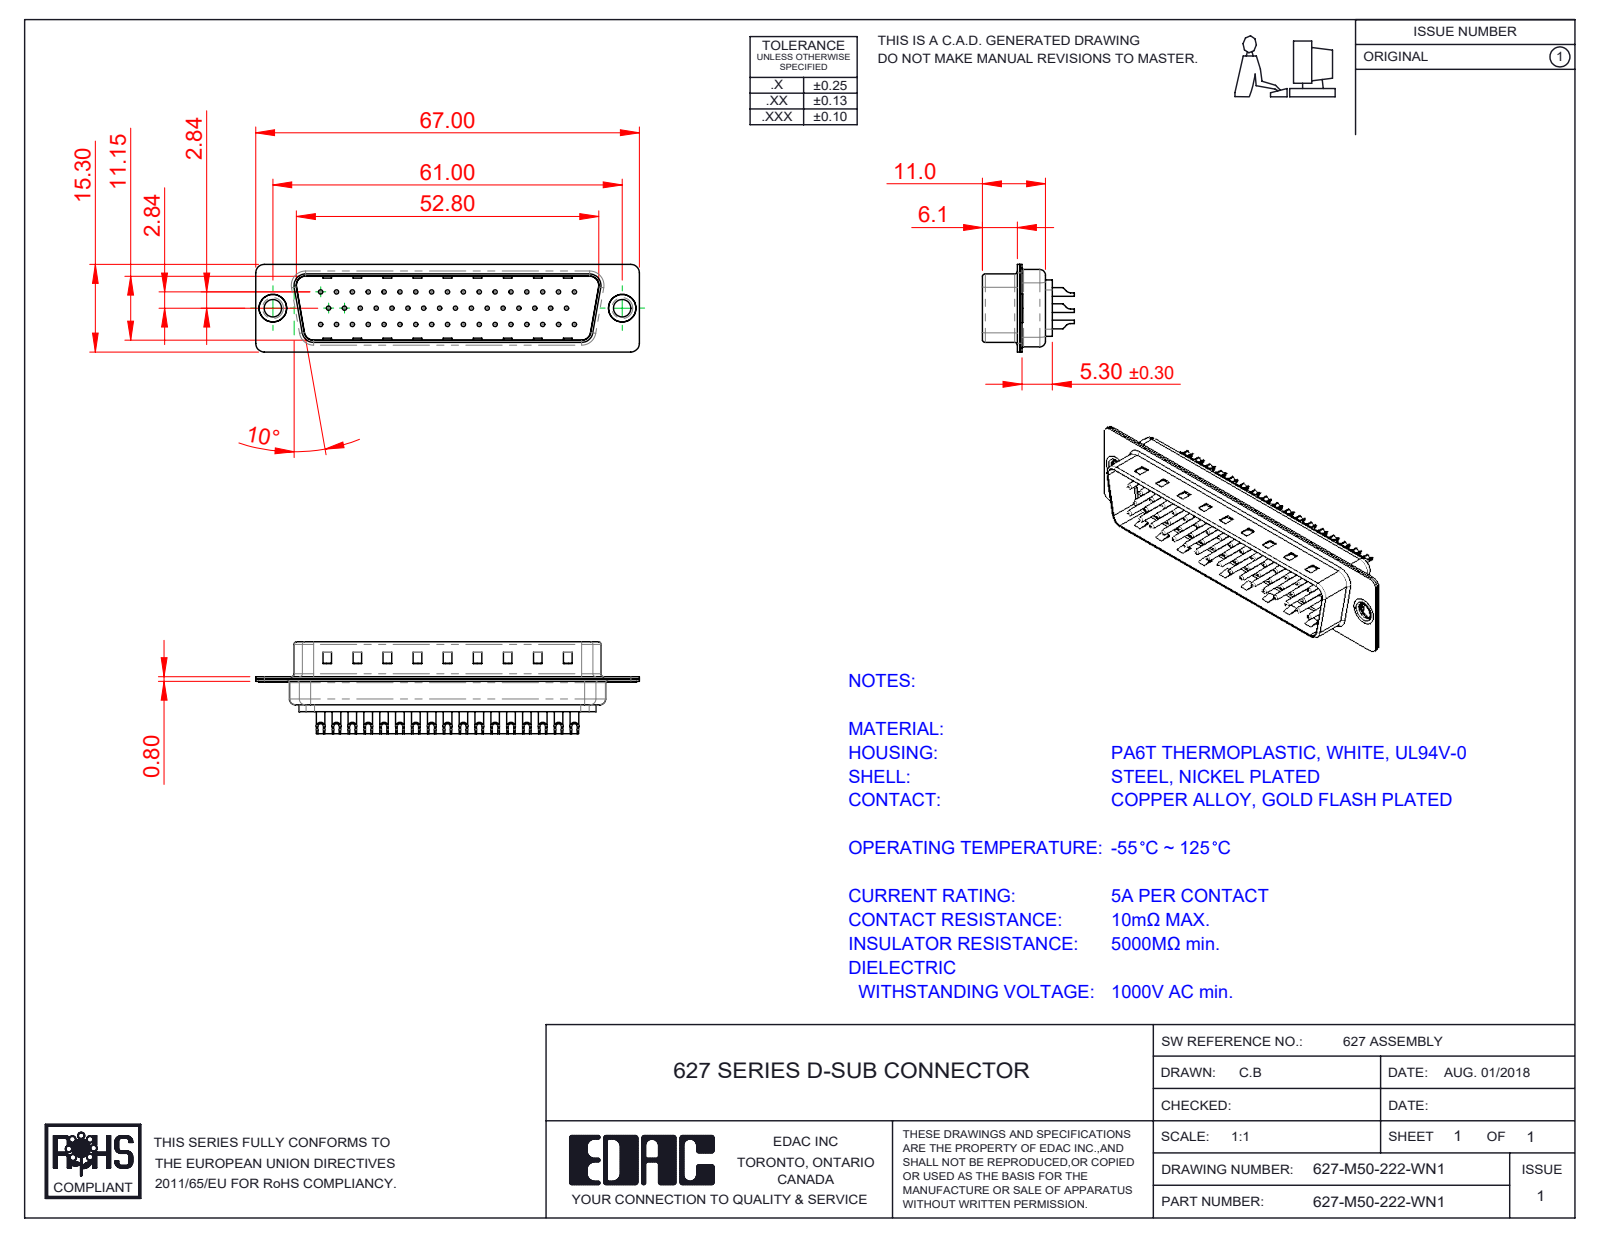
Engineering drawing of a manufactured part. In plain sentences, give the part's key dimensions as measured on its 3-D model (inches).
The part is named "627M Contact Row 3_22; 627-M50-222-WN1; 627M Shell Rear_50 Contacts; 627M Housing_50 Contacts (+4 more)". Its 3-D file was written by "SolidWorks 2020 (CONFIG_CONTROL_DESIGN)". It is 55 solids with 2236 faces: 653 planar, 925 cylindrical and 658 other. Overall it measures 2.638 by 0.632 by 0.602 inches. Its volume is 0.278 cubic inches and its surface area 17.08 square inches. Round holes: 50 of diameter 0.03, 50 of diameter 0.039, 50 of diameter 0.063, 50 of diameter 0.079, 2 of diameter 0.12, 2 of diameter 0.157, 2 of diameter 0.189. Round bosses or shafts: 50 of diameter 0.059, 2 of diameter 0.197, 2 of diameter 0.193, 2 of diameter 0.14. Partial cylindrical surfaces (rounded edges, fillets, slot ends): 16 of radius 0.059, 12 of radius 0.079, 8 of radius 0.02, 8 of radius 0.063, 7 of radius 0.039, 4 of radius 0.01, 4 of radius 0.024, 4 of radius 0.026. The main face-to-face distances are 0.016, 0.455, 0.224, 0.24, 0.031, 0.03, 0.485, 0.485, 0.516, 0.209. The hole center spacings are 0.124, 0.109, 0.218, 0.327, 0.436, 0.545, 0.654, 0.198.
